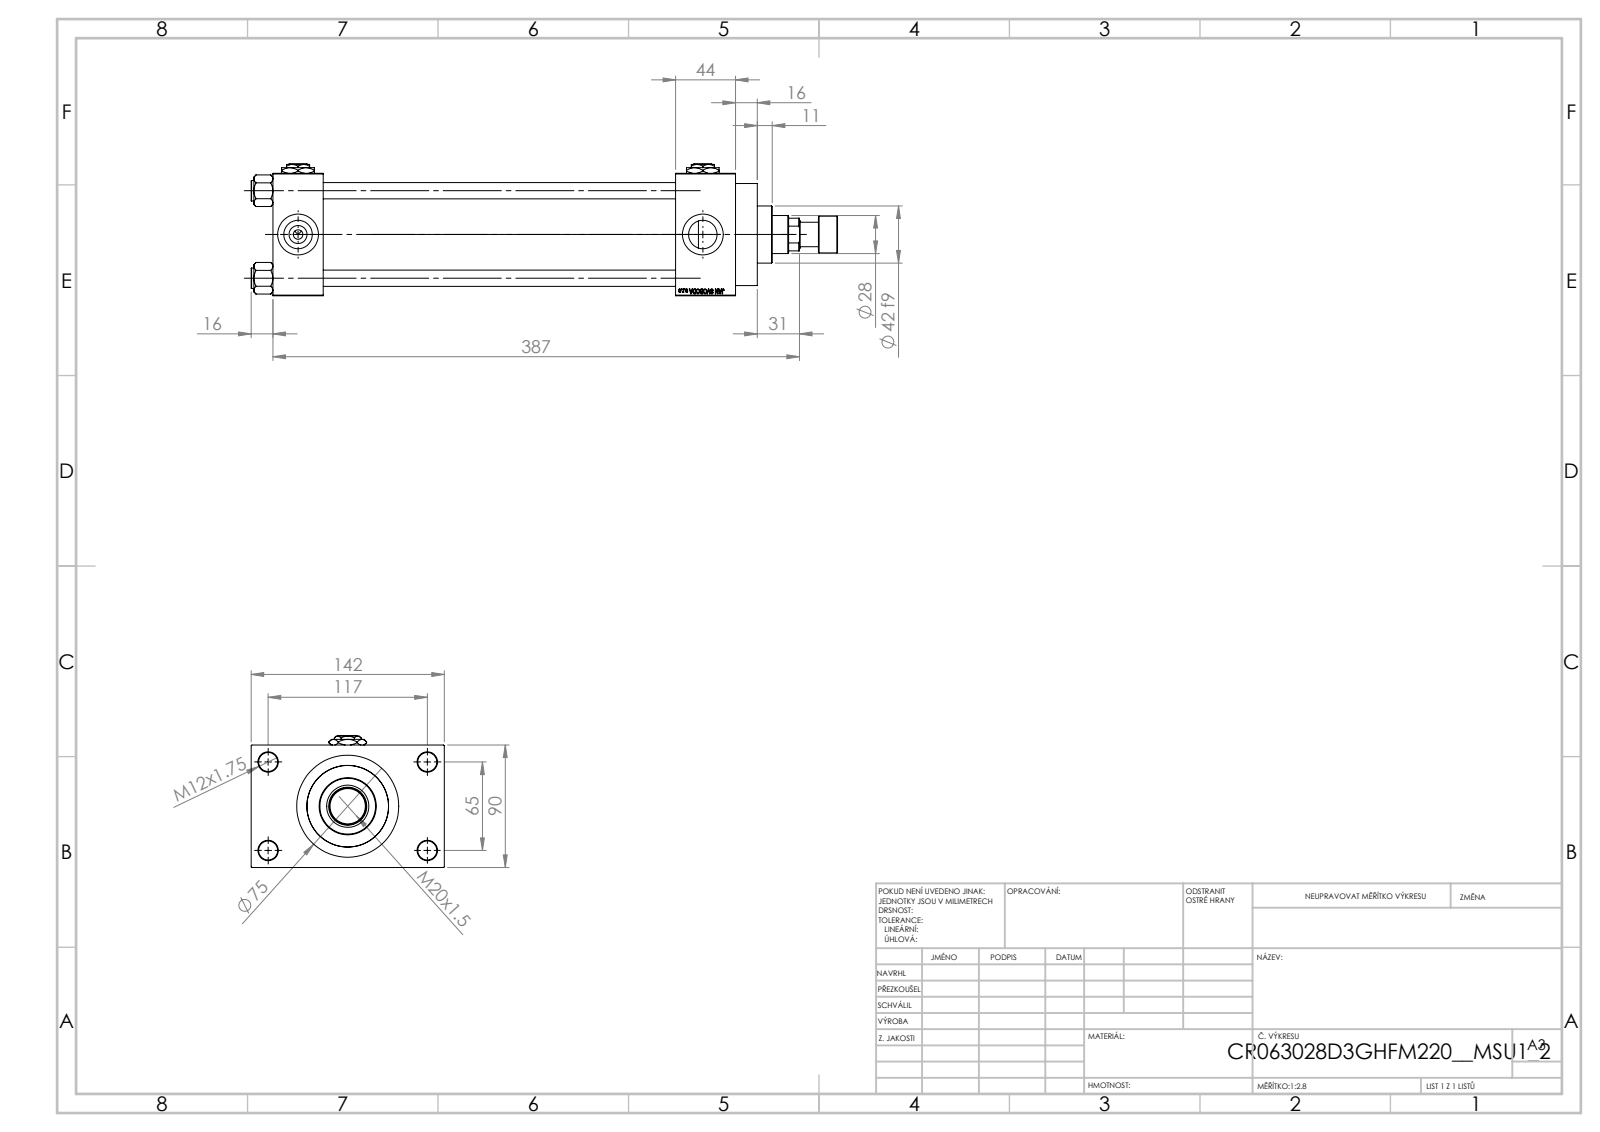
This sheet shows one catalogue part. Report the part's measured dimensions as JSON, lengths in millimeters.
{"part_name": "V215CR_D_Body; V215_VC_A; V215CR_ROD_END_F; V215CR_VCP_D (+3 more)", "step_written_by": "SolidWorks 2019 (CONFIG_CONTROL_DESIGN)", "units": "millimeters", "bodies": {"solids": 14, "faces": 1218, "planar": 549, "cylindrical": 103, "other": 566}, "overall_size": [431, 142, 97], "volume_mm3": 1440000, "surface_area_mm2": 338888, "round_holes": [[12, 4], [14, 4], [20.96, 4], [30, 4], [7, 3], [18.5, 1], [28, 1], [31, 1], [50, 1], [60, 1], [63, 1]], "round_bosses_or_shafts": [[15, 4], [75, 1], [69, 1], [42, 1], [27, 1], [18, 1]], "face_to_face_distances": [90, 259, 37, 296, 303, 340, 44, 26, 116, 16], "hole_center_spacings": [26.35, 45.47, 64.3, 66.92, 69.81, 90.65, 111.34, 65]}
